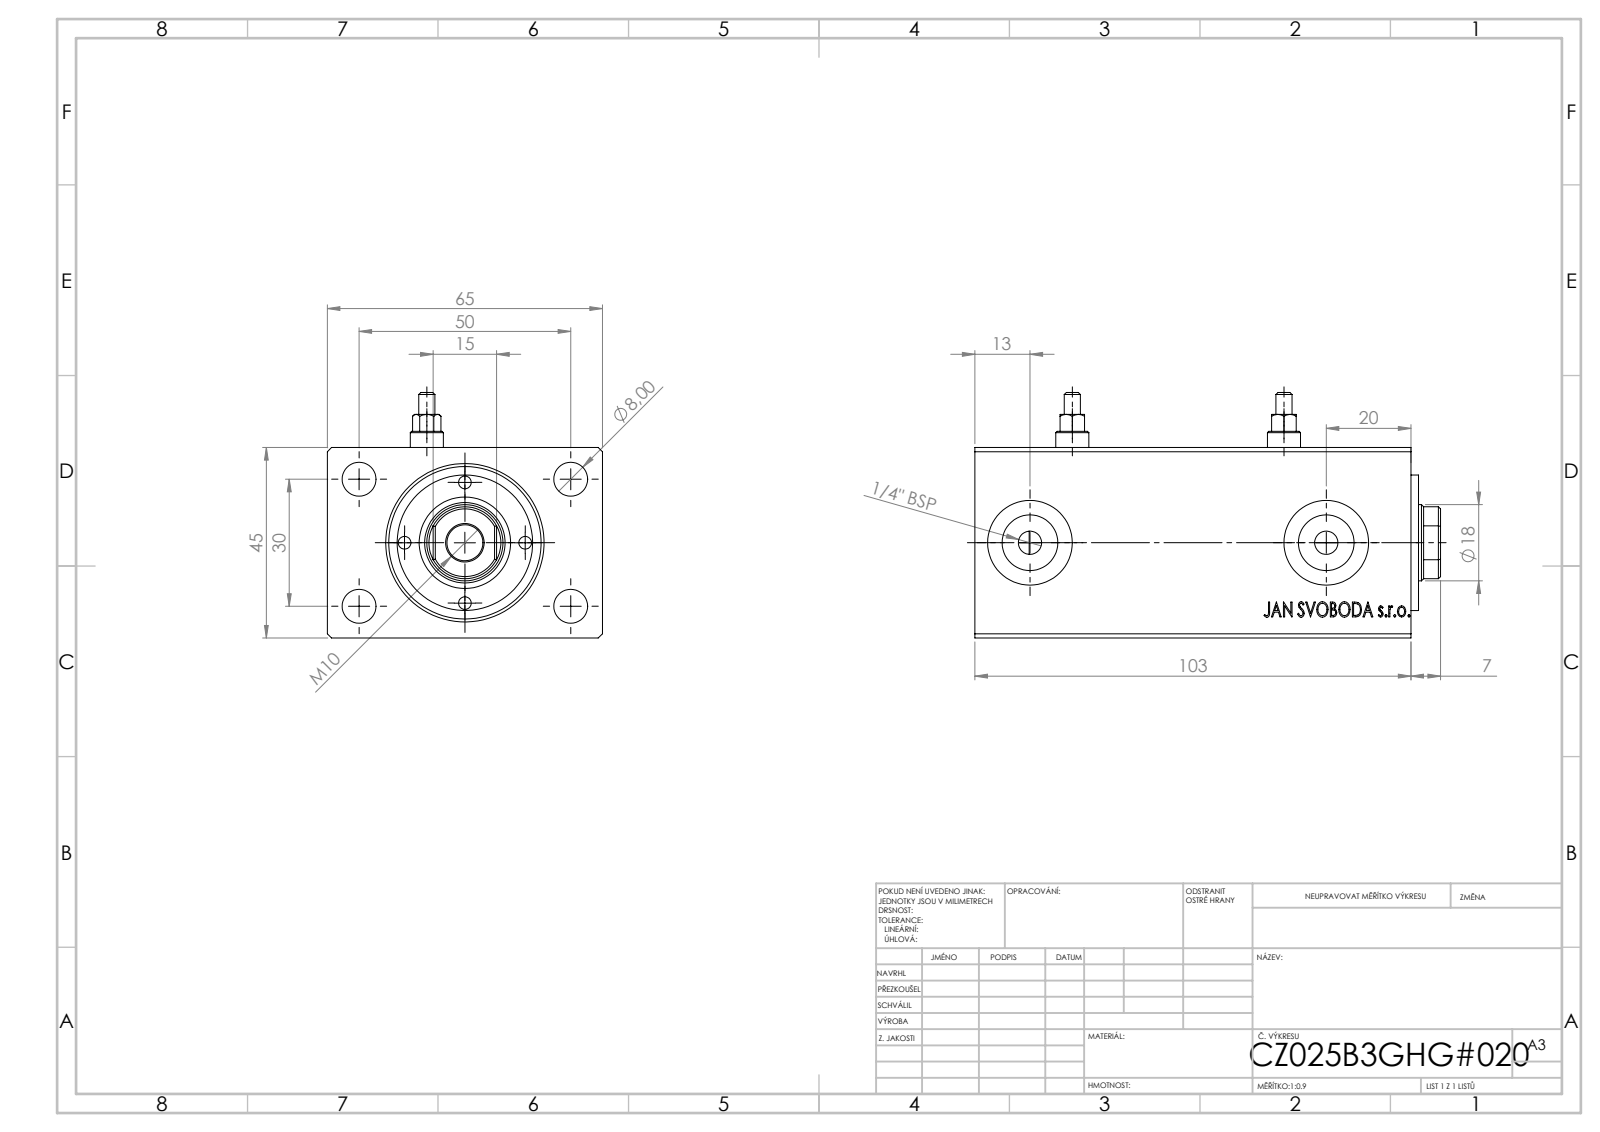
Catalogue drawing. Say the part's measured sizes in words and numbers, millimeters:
The part is named "V500CZ; Zatka_Cushioning3; V500CZ_B_VC". Its 3-D file was written by "SolidWorks 2019 (CONFIG_CONTROL_DESIGN)". It is 5 solids with 933 faces: 423 planar, 74 cylindrical and 436 other. Overall it measures 110 by 65 by 58 millimeters. Its volume is 282 743 cubic millimeters and its surface area 53 676 square millimeters. Round holes: 6 of diameter 8, 4 of diameter 3, 2 of diameter 1.8, 2 of diameter 5.5, 2 of diameter 13.16, 2 of diameter 20, 1 of diameter 8.5, 1 of diameter 18, 1 of diameter 19, 1 of diameter 25, 1 of diameter 36. Round bosses or shafts: 2 of diameter 7.8, 2 of diameter 3.8, 1 of diameter 32. Partial cylindrical surfaces (rounded edges, fillets, slot ends): 1 of radius 8.5. The main face-to-face distances are 45, 65, 103, 7, 102.8, 12.8, 90.2, 12.6, 1.8, 5.2. The hole center spacings are 14.25, 18.45, 20.15, 25.01, 29.15, 38.48, 42.02, 50.
